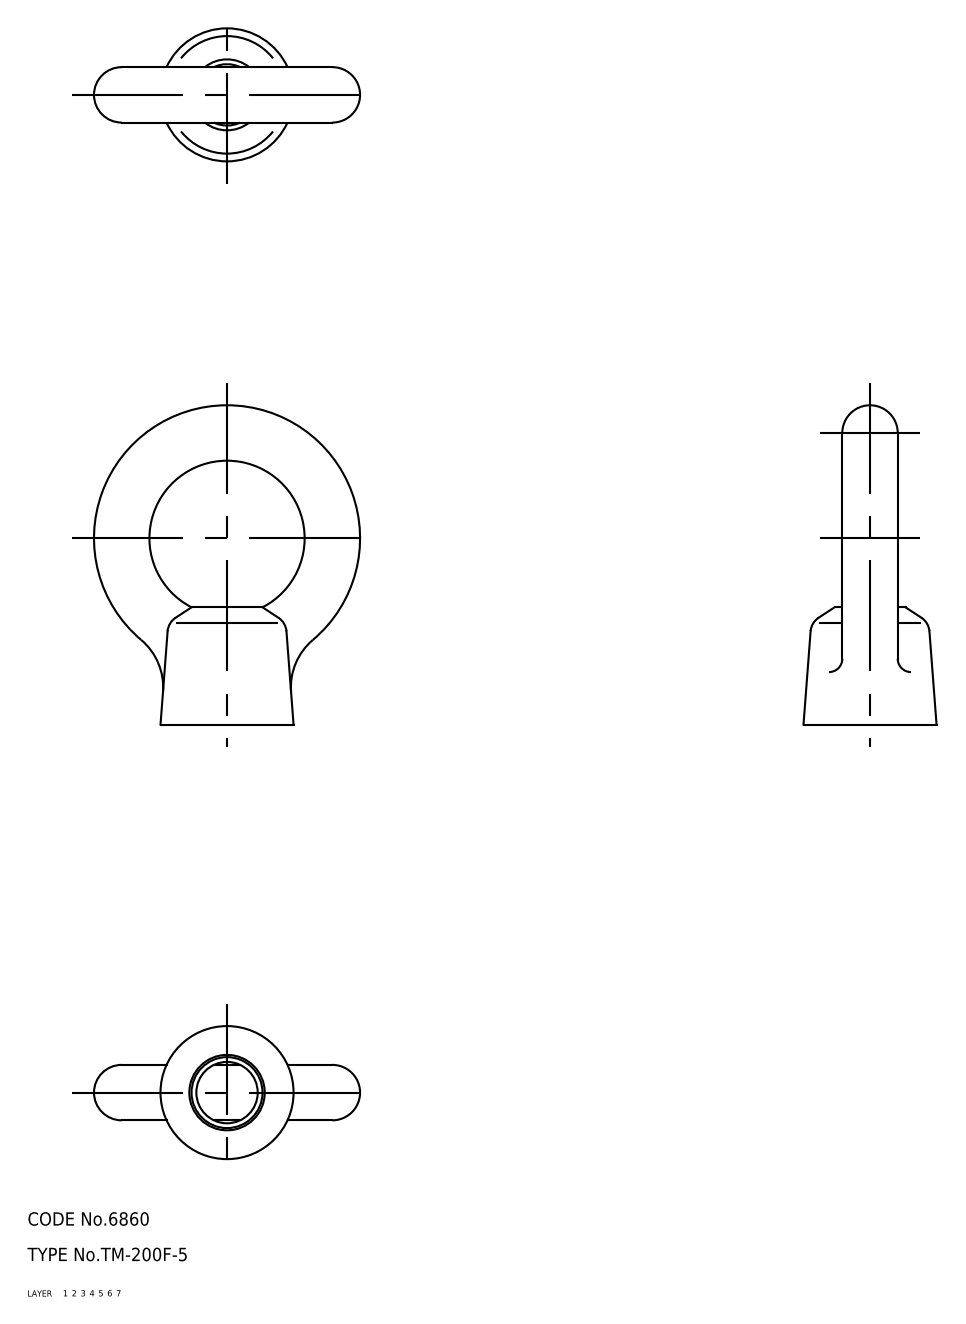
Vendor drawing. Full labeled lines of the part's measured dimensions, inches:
Part name (STEP PRODUCT): TM_200F_5
STEP written by: SolidWorks 2003240 (AUTOMOTIVE_DESIGN)
Units: inches
Bodies: 1 solid, 19 faces (1 planar, 2 cylindrical, 16 other)
Overall size (bounding box): 2.835 × 2.362 × 1.181
Volume: 1.586 in³ · Surface area: 13.83 in²
Round holes (diameter × count): ⌀0.63 ×1
